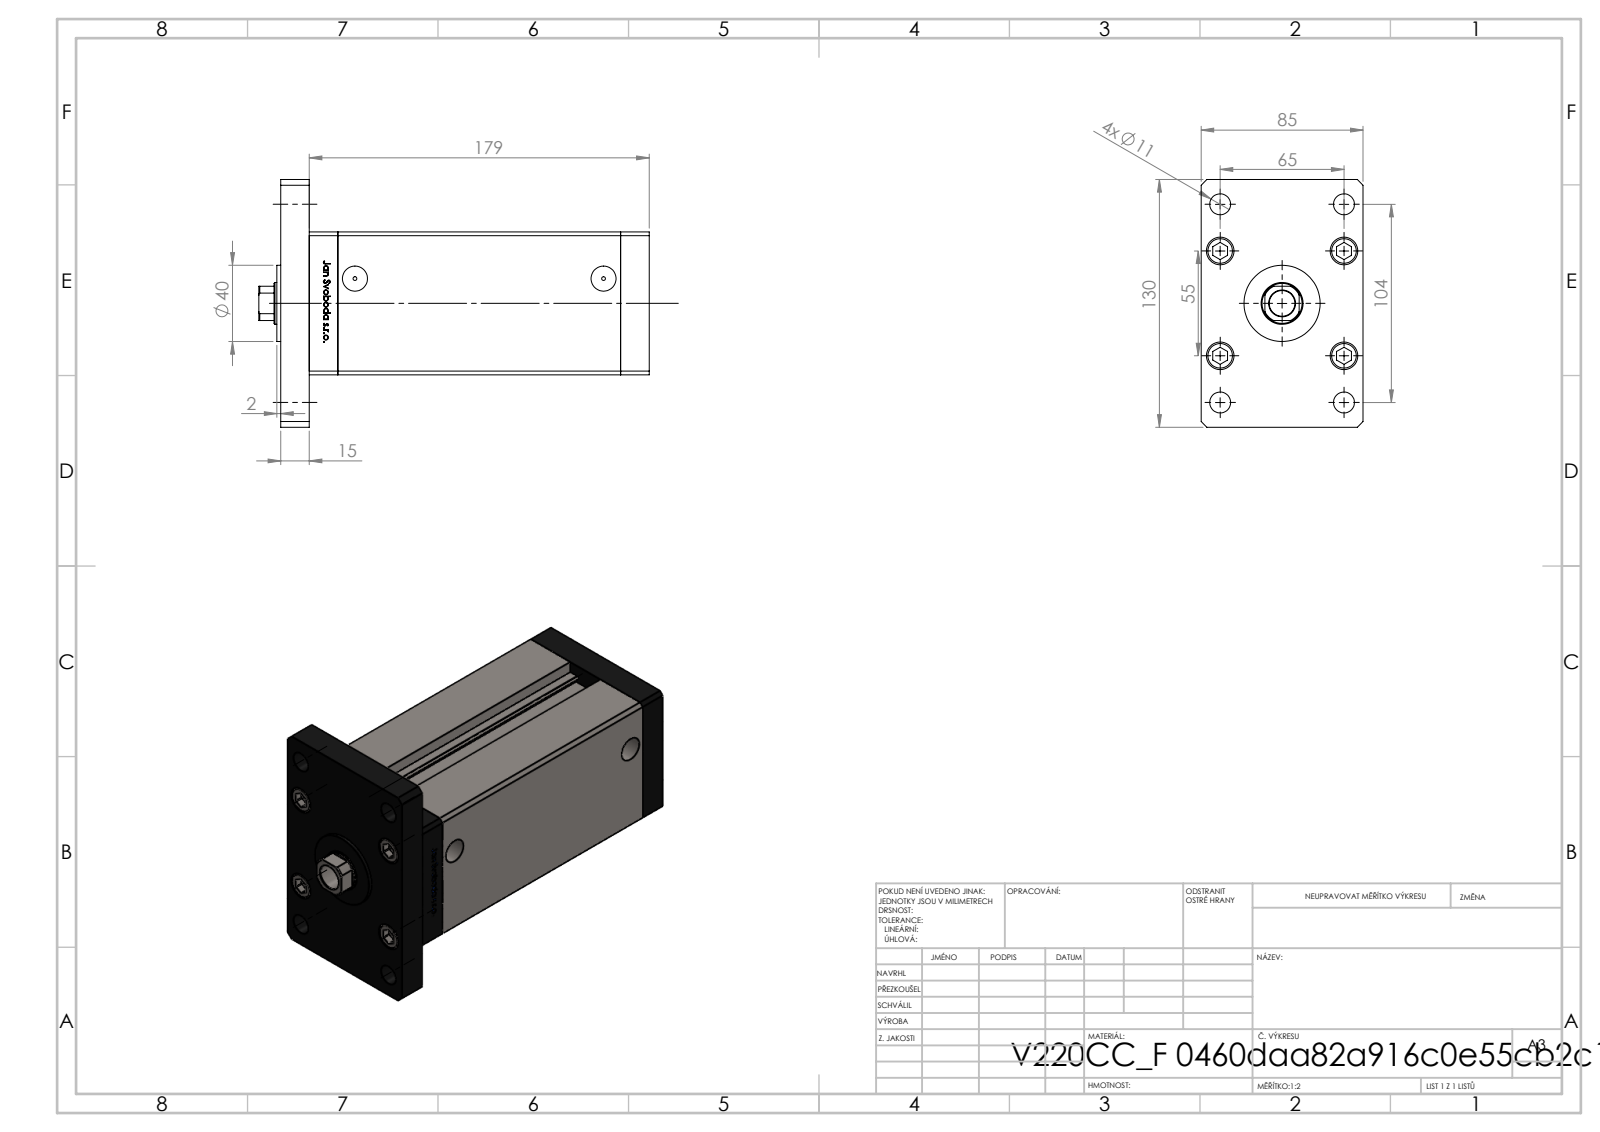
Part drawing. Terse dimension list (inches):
name: V220C_F_MIDDLE; V220C_VC_F; V220C_FRONT_F; V220C BACK_F (+2 more)
written by: SolidWorks 2019 (CONFIG_CONTROL_DESIGN)
unit: in
bodies: 19 solids, 1308 faces (515 planar, 187 cylindrical, 606 other)
size: 8.071 × 5.118 × 3.346
volume: 71.09 in³; area: 308.2 in²
holes: 9× ⌀0.433, 5× ⌀0.61, 4× ⌀0.394, 4× ⌀0.571, 2× ⌀0.079, 2× ⌀0.518, 1× ⌀0.531, 1× ⌀0.866, 1× ⌀0.925
bosses: 9× ⌀0.315, 5× ⌀0.571, 1× ⌀1.575
rounds: 2× R0.037, 1× R0.413
face distances: 0.591, 3.346, 6.437, 7.028, 2.953, 5.846, 1.181, 7.618, 0.413, 1.083
hole spacings: 1.102, 0.965, 1.676, 2.414, 2.559, 2.735, 3.13, 4.043
